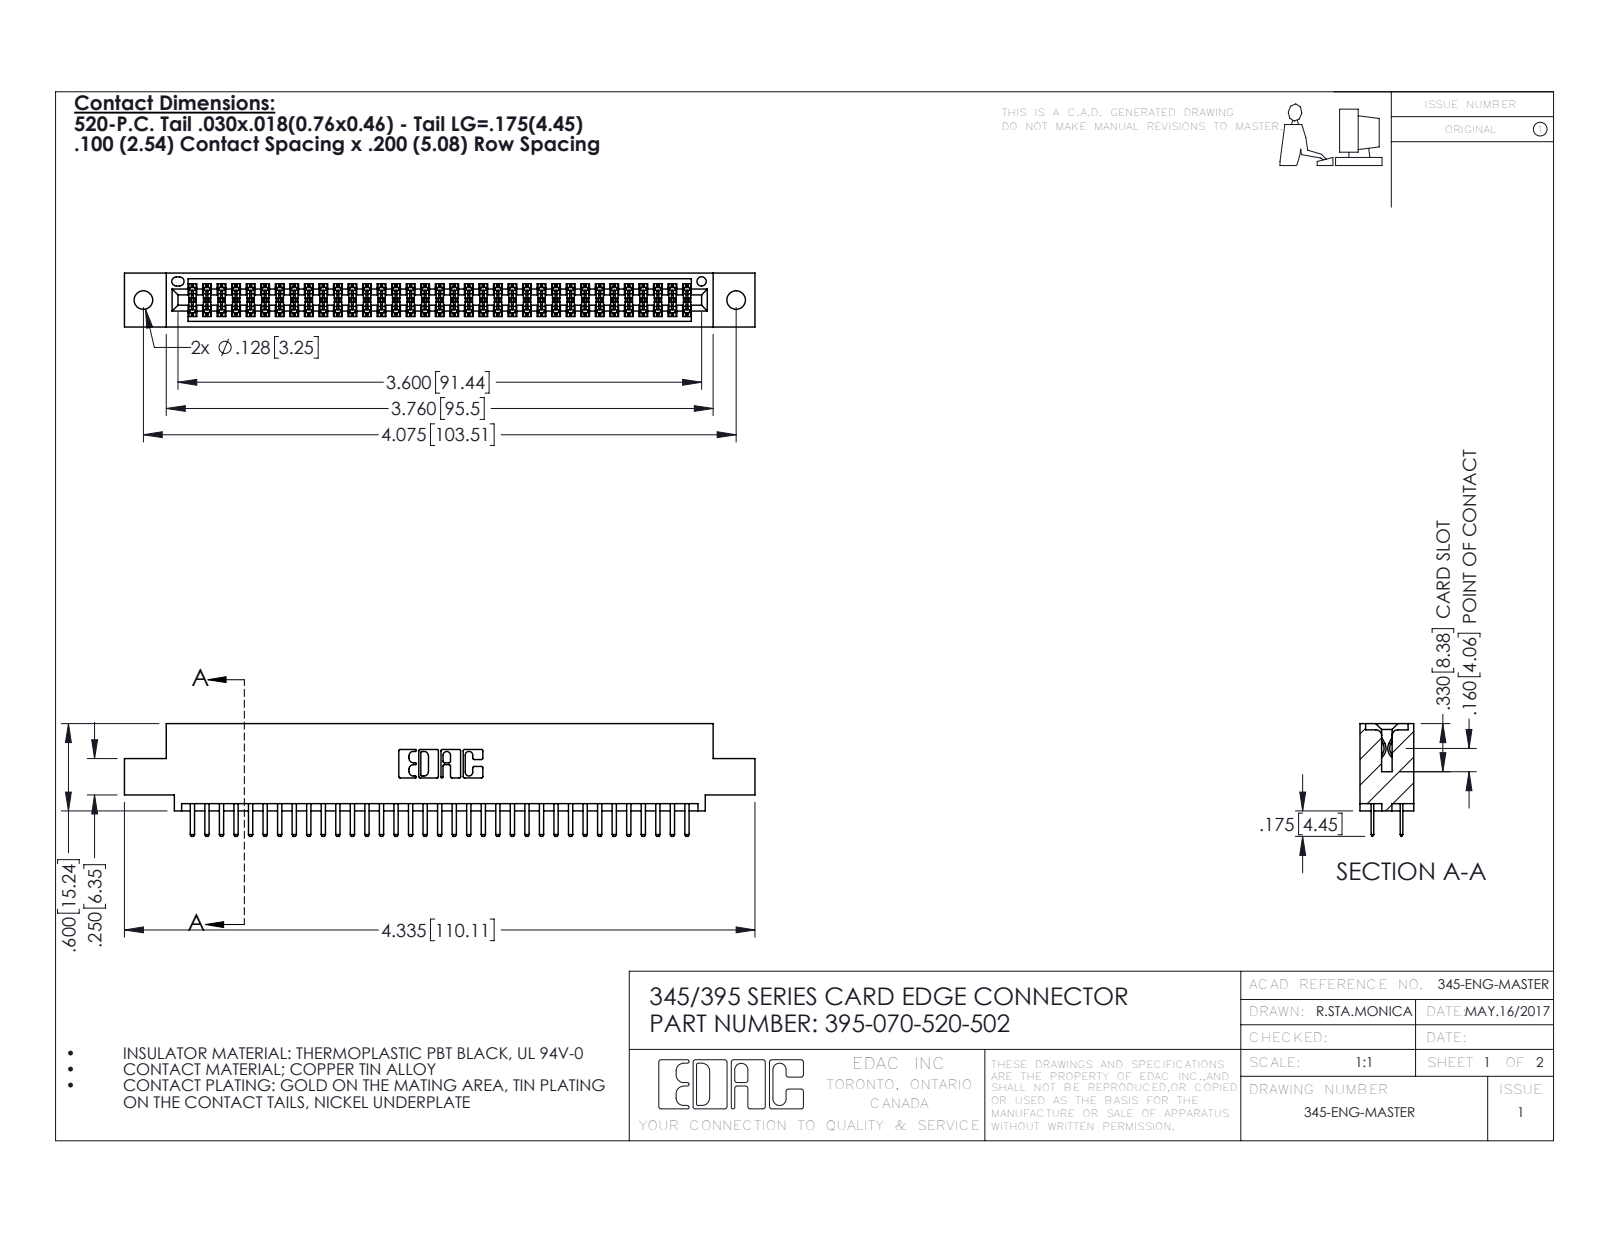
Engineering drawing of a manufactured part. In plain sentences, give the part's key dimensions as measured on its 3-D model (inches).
The part is named "345-292-001_345-293-120; 345 Part_0.110 Offset - 0.128 Dia; 395-070-520-502". Its 3-D file was written by "SolidWorks 2016 (CONFIG_CONTROL_DESIGN)". It is 71 solids with 3910 faces: 2534 planar, 1376 cylindrical and 0 other. Overall it measures 4.335 by 0.775 by 0.37 inches. Its volume is 0.64 cubic inches and its surface area 23.44 square inches. Round holes: 2 of diameter 0.128, 1 of diameter 0.064. Partial cylindrical surfaces (rounded edges, fillets, slot ends): 105 of radius 0.006, 74 of radius 0.01, 22 of radius 0.01, 6 of radius 0.007, 6 of radius 0.031, 3 of radius 0.026, 2 of radius 0.014, 2 of radius 0.019. The main face-to-face distances are 0.298, 0.072, 0.2, 0.37, 0.098, 0.272, 0.025, 0.225, 0.022, 0.072. The hole center spacings are 0.27, 3.839, 4.075.
